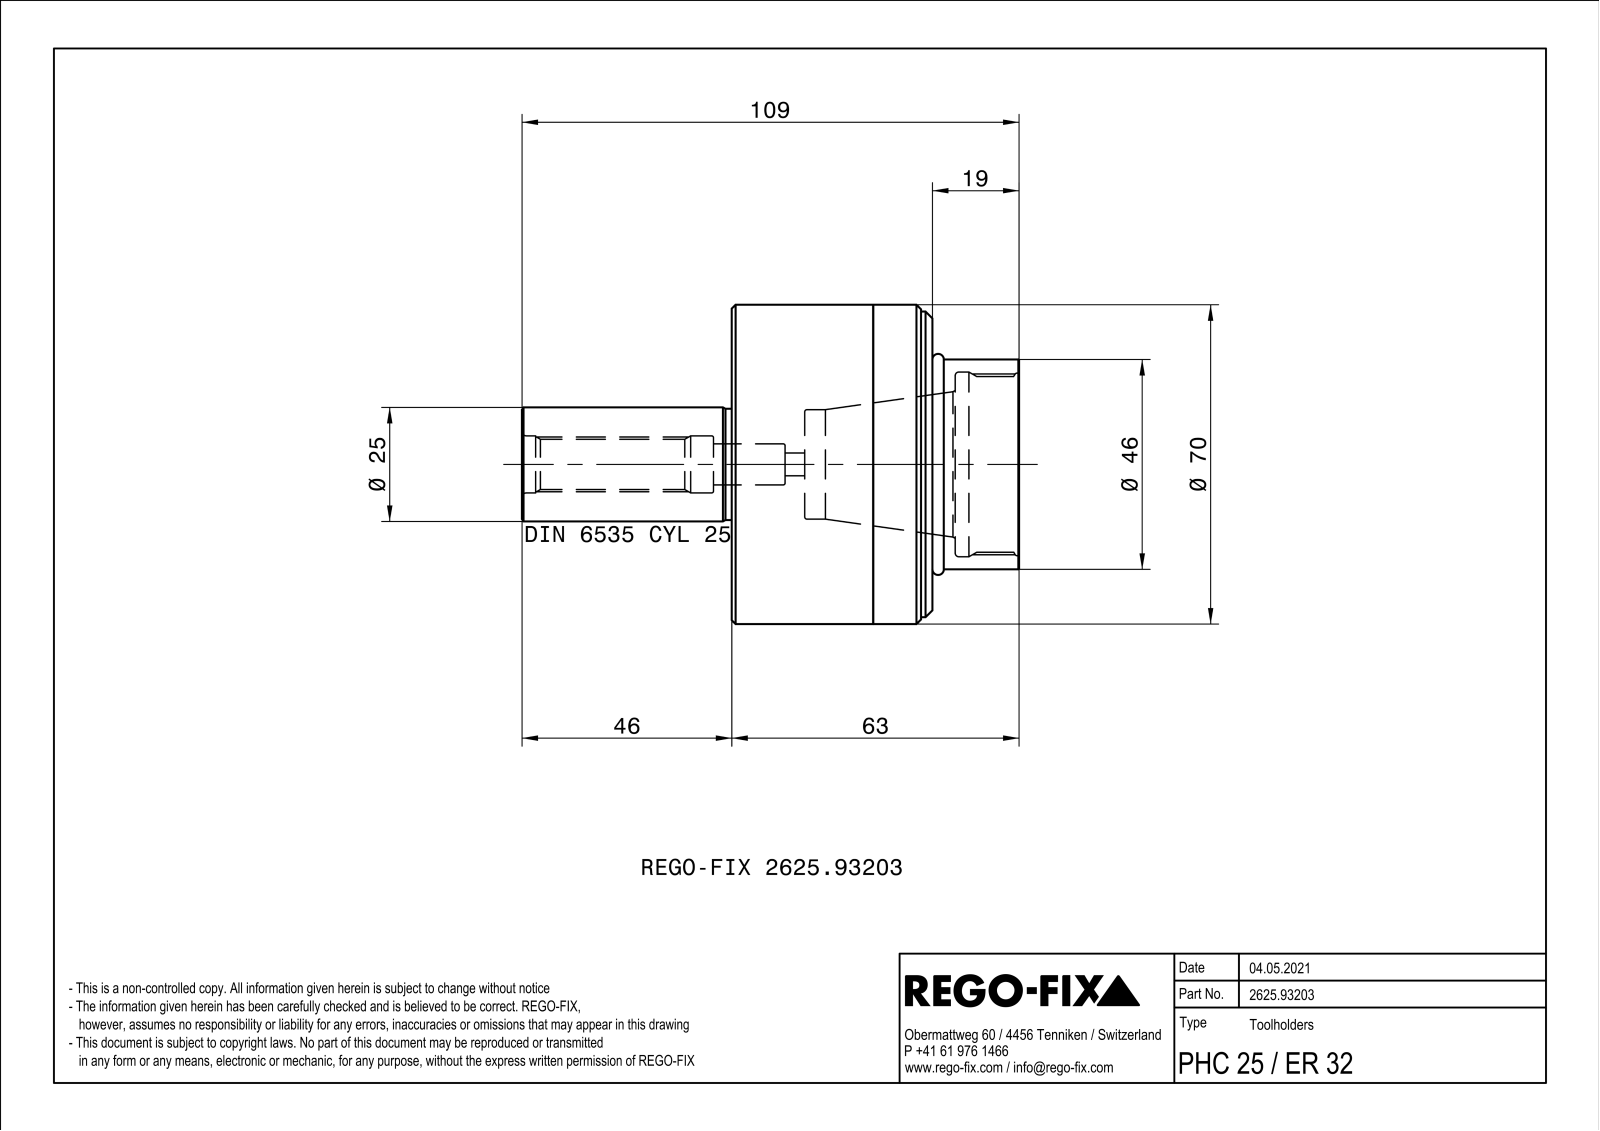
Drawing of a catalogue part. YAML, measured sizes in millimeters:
part_name: "NOCUT"
step_written_by: "SIEMENS PLM Software Solid Edge ST10 (AUTOMOTIVE_DESIGN)"
units: millimeters
bodies: {solids: 1, faces: 128, planar: 27, cylindrical: 37, other: 64}
overall_size: [109, 70, 70]
volume: 143603
surface_area: 53286
round_holes:
  - {diameter: 5, count: 4}
  - {diameter: 2.11, count: 1}
  - {diameter: 3.2, count: 1}
  - {diameter: 5.2, count: 1}
  - {diameter: 7.4, count: 1}
  - {diameter: 9, count: 1}
  - {diameter: 11, count: 1}
  - {diameter: 12.5, count: 1}
  - {diameter: 24, count: 1}
  - {diameter: 38.5, count: 1}
  - {diameter: 40.5, count: 1}
  - {diameter: 46, count: 1}
round_bosses_or_shafts:
  - {diameter: 70, count: 1}
  - {diameter: 67, count: 1}
  - {diameter: 60, count: 1}
  - {diameter: 58.5, count: 1}
  - {diameter: 58.4, count: 1}
  - {diameter: 54, count: 1}
  - {diameter: 53.4, count: 1}
  - {diameter: 36, count: 1}
face_to_face_distances: [6, 12, 5.7, 12.3, 6.3, 26, 18, 32, 44, 38.3]
hole_center_spacings: [24, 33.94, 48, 27.8]
